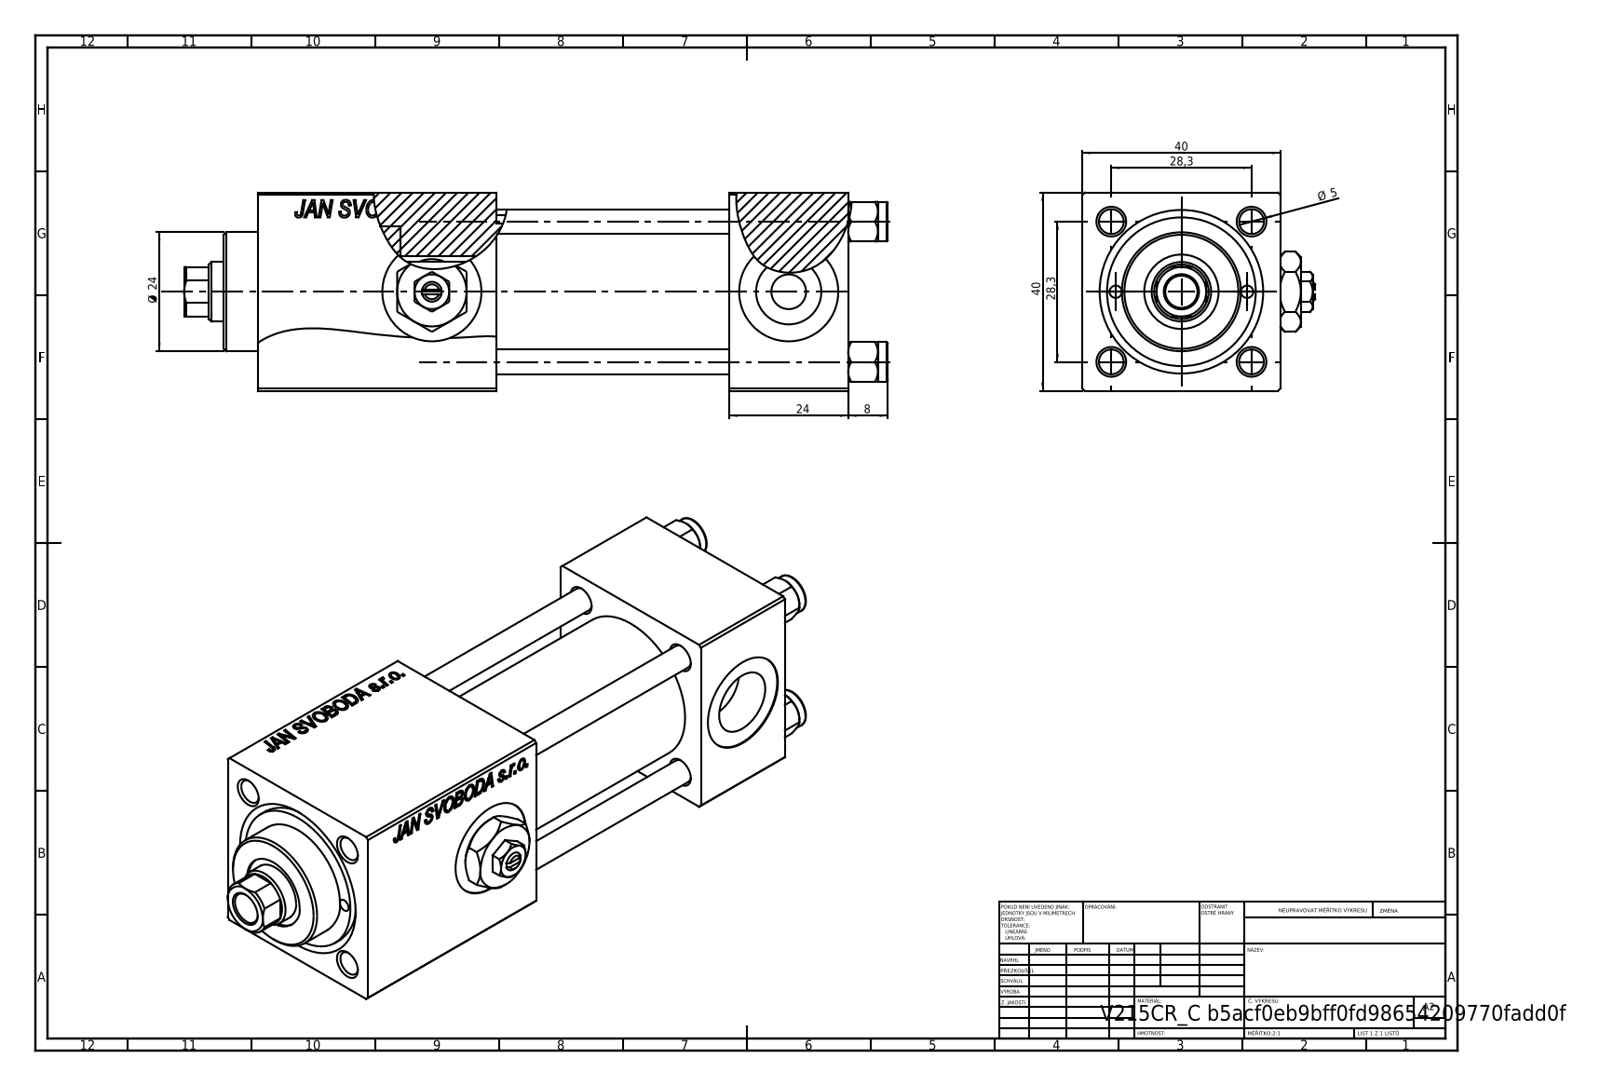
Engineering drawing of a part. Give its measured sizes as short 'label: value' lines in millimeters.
name: NUT_M5_C; V215CR_VCP_C; V215_VC_A; V215CR_C_TYCINKA (+2 more)
written by: SolidWorks 2019 (CONFIG_CONTROL_DESIGN)
unit: mm
bodies: 12 solids, 1201 faces (551 planar, 94 cylindrical, 556 other)
size: 142 × 47 × 40
volume: 141 941 mm³; area: 55 199 mm²
holes: 4× ⌀5, 3× ⌀20, 2× ⌀2.5, 2× ⌀7, 2× ⌀13.16, 1× ⌀6.5, 1× ⌀12, 1× ⌀15, 1× ⌀25, 1× ⌀30
bosses: 4× ⌀8, 1× ⌀31, 1× ⌀24
rounds: 1× R5.5
face distances: 40, 24, 90.3, 66.3, 48, 47, 71, 19.3, 119, 95
hole spacings: 14.18, 20.01, 28.3, 30.84, 13.25, 40.02, 26.5, 72
